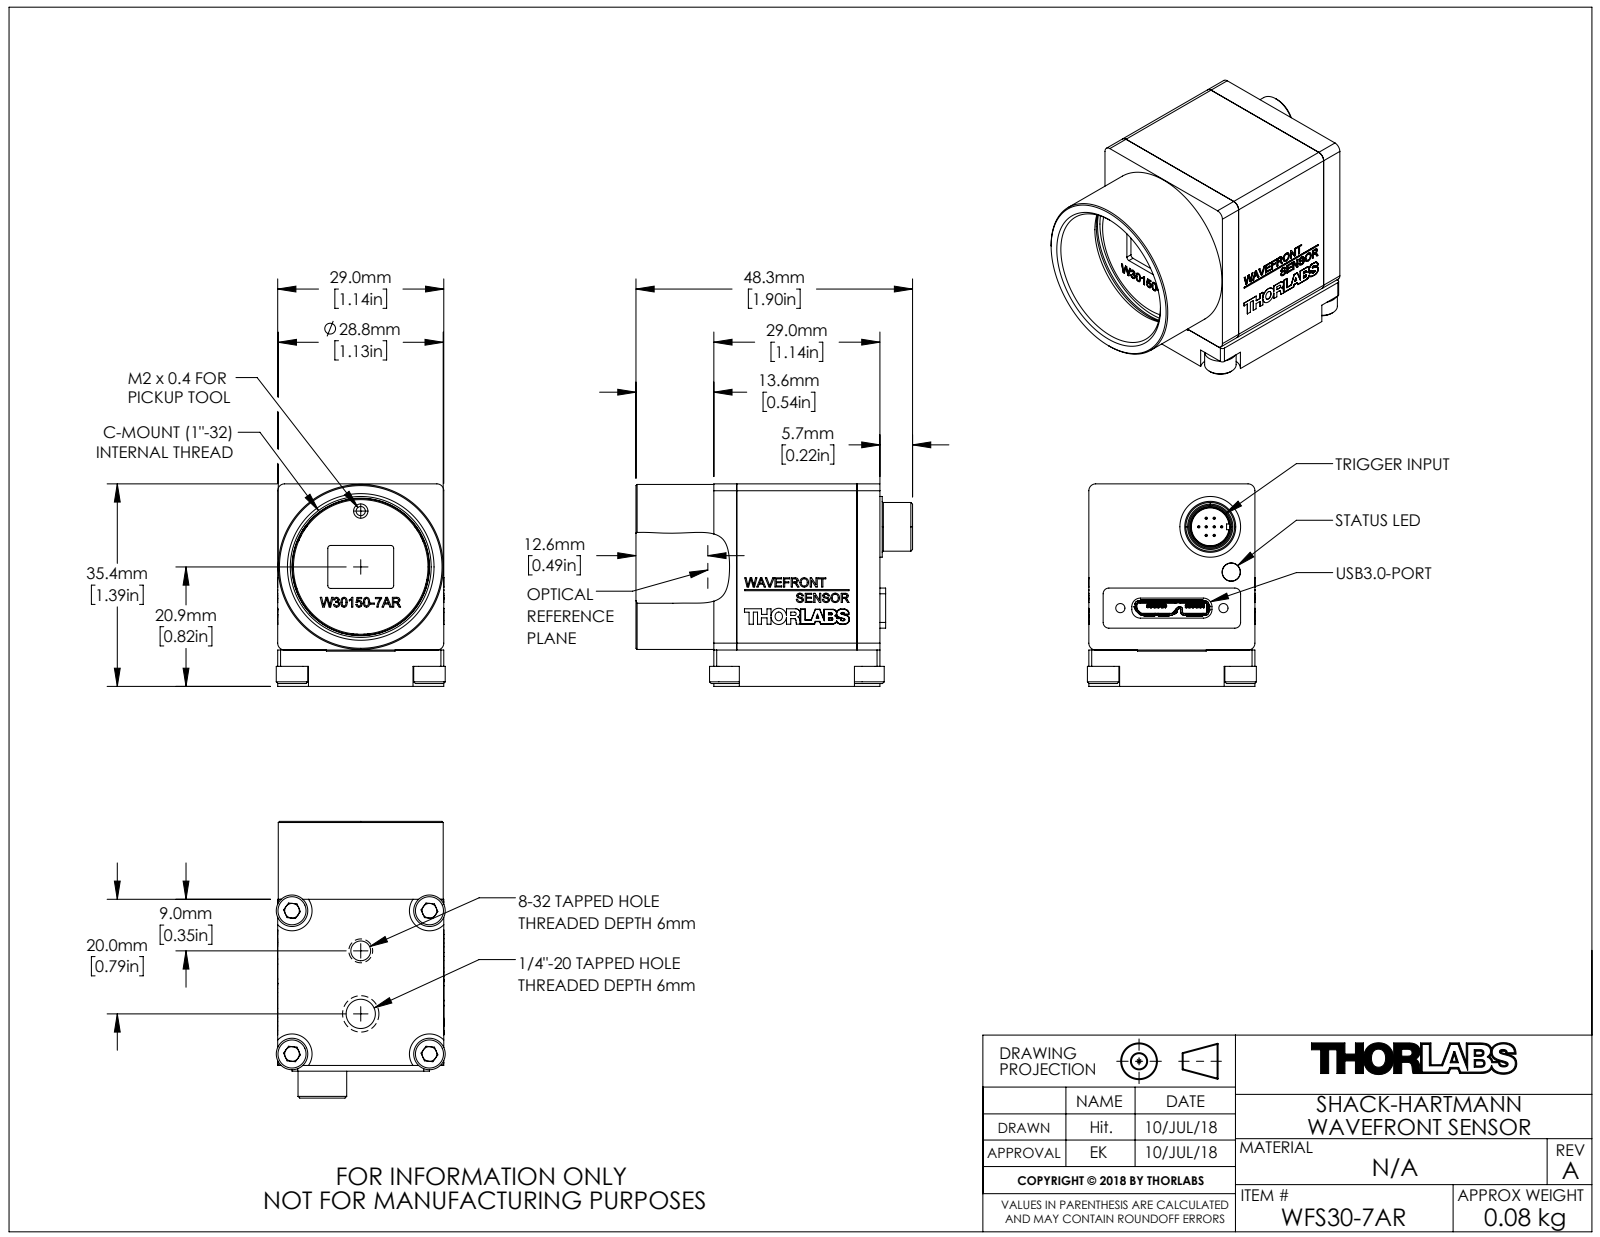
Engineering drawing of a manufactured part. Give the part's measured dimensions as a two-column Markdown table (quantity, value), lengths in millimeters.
| quantity | value |
| --- | --- |
| part name | MTN008511-E0W |
| STEP written by | SolidWorks 2016 (AUTOMOTIVE_DESIGN) |
| units | millimeters |
| bodies | 0 solids, 2610 faces (1900 planar, 405 cylindrical, 305 other) |
| overall size | 48.3 × 35.35 × 29.5 |
| round holes (diameter × count) | 3.2 × 11, 2.5 × 5, 1.6 × 3, 1.9 × 3, 0.95 × 1, 1.5 × 1, 3.45 × 1, 5.11 × 1, 6.8 × 1, 8 × 1, 15 × 1, 24 × 1 |
| round bosses / shafts (diameter × count) | 0.4 × 8, 1 × 6, 3 × 5, 5.5 × 4, 28.8 × 1, 23.9 × 1, 23.5 × 1, 10.6 × 1 |
| partial cylindrical surfaces (radius × count) | 0.5 × 37, 0.2 × 31, 0.15 × 29, 0.3 × 12, 1 × 11, 1.5 × 10, 0.1 × 8, 0.6 × 8 |
| main face-to-face distances | 29, 0.6, 28.4, 6.35, 1, 4.8, 35.35, 2.62, 27.8, 17.57 |
| hole center spacings | 9.75, 18.83, 9.74, 13.79, 16.88, 5.04, 13.89, 21.63 |
